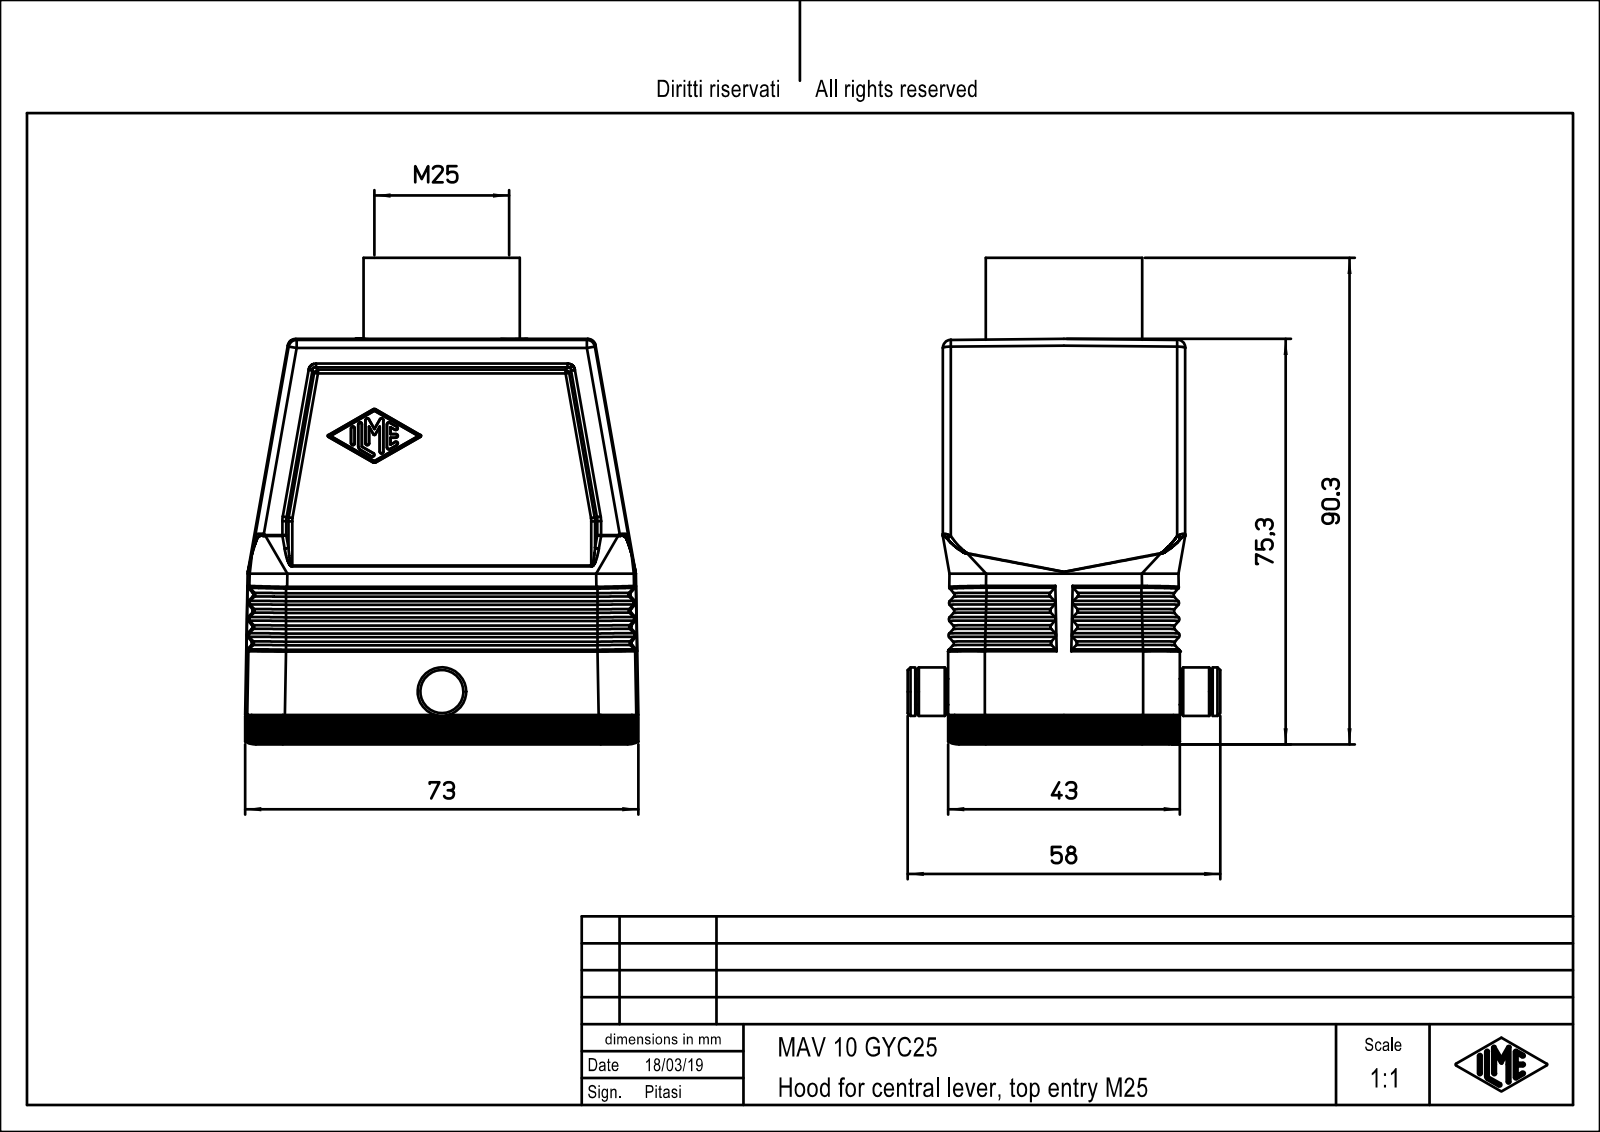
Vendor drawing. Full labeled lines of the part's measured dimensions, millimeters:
Part name (STEP PRODUCT): MAV_10_GYC25
STEP written by: PTC Creo Elements/Direct Modeling 19.0E 27-Jun-2016 (C) Parametric Technology GmbH (AUTOMOTIVE_DESIGN)
Units: millimetres
Bodies: 1 solid, 499 faces (159 planar, 140 cylindrical, 200 other)
Overall size (bounding box): 90.25 × 73 × 58
Volume: 82 914 mm³ · Surface area: 39 549 mm²
Round holes (diameter × count): ⌀3 ×4, ⌀20 ×1
Round bosses / shafts (diameter × count): ⌀29 ×1, ⌀25 ×1, ⌀9 ×1, ⌀4.8 ×1
Partial cylindrical surfaces — rounded edges, fillets, slot ends (radius × count): R1 ×32, R0.5 ×16, R7 ×12, R1.5 ×10, R3 ×8, R3.5 ×4, R4 ×4, R4.2 ×4
Main face-to-face distances: 43, 4, 1.05, 2, 7, 1, 44, 6.5, 39, 5
Hole centre spacings: 31.54, 27, 57, 63.07
